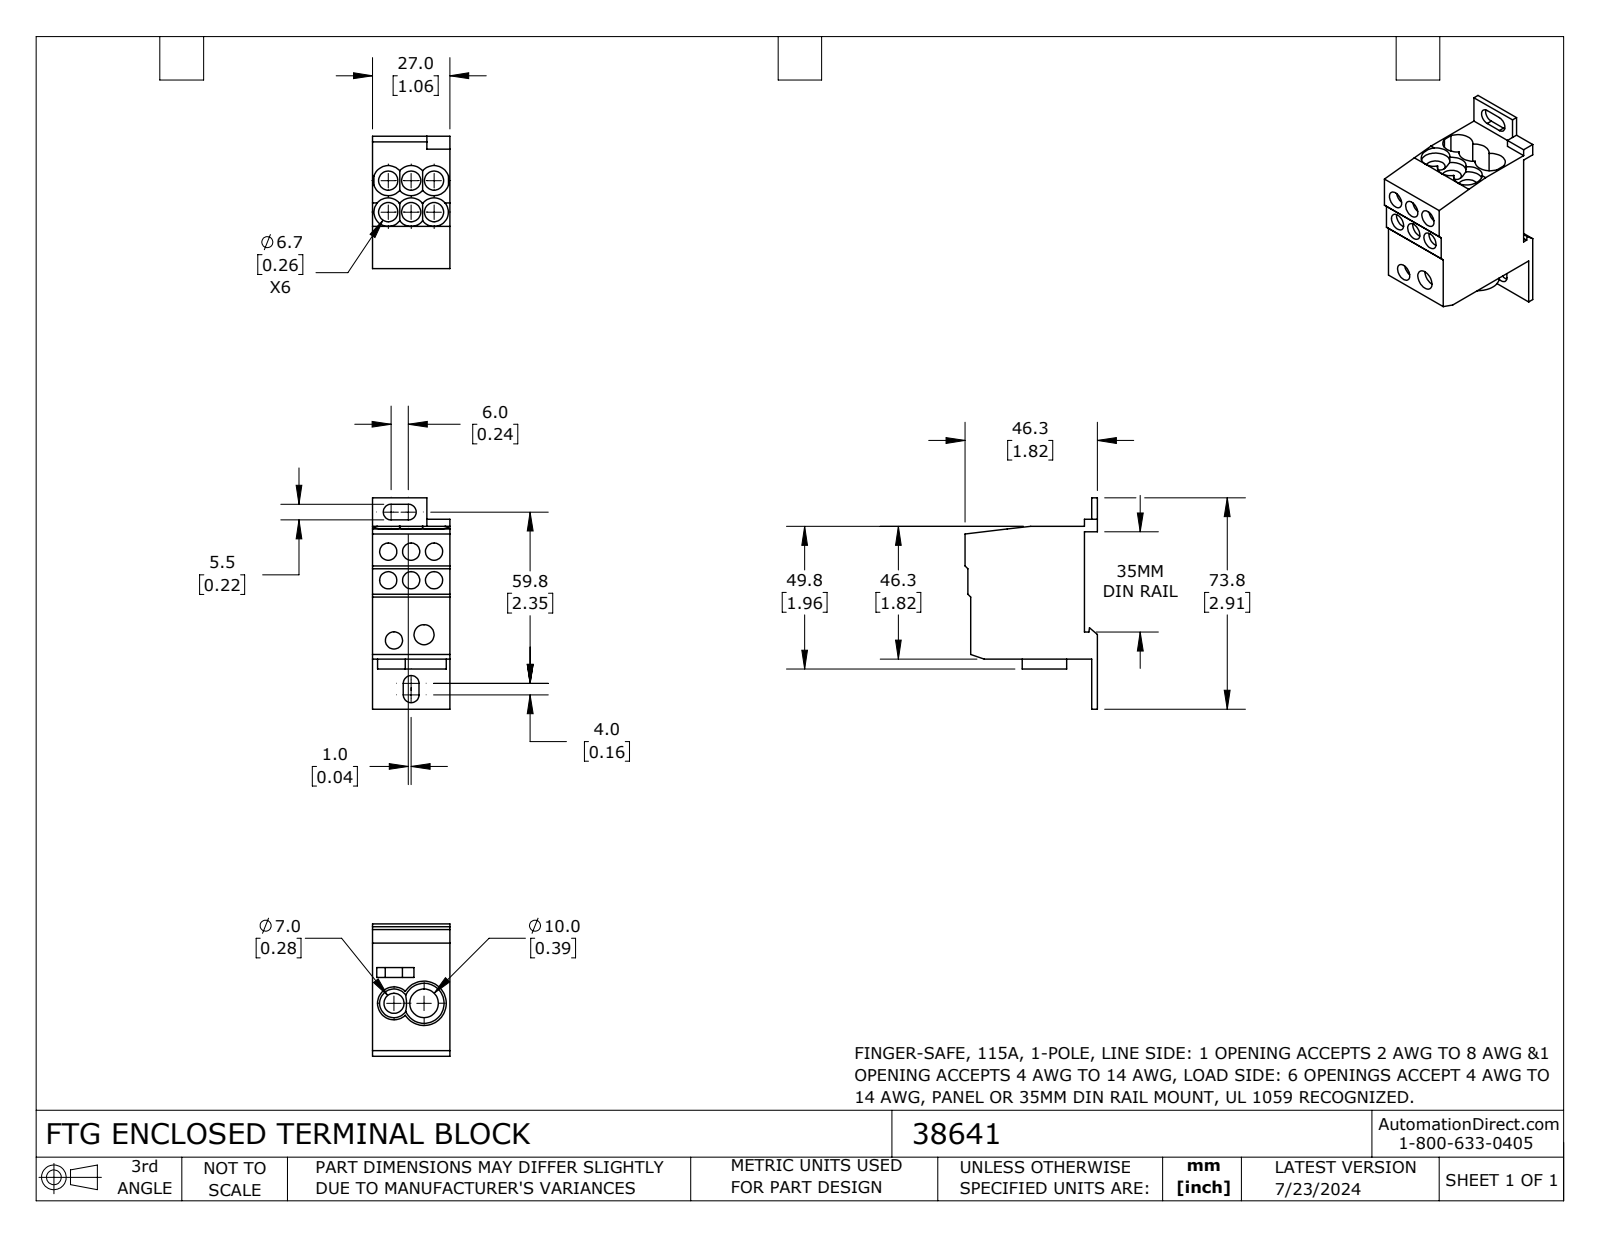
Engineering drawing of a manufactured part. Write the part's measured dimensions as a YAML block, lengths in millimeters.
part_name: "38641"
step_written_by: "SolidWorks 2023 (CONFIG_CONTROL_DESIGN)"
units: millimeters
bodies: {solids: 1, faces: 131, planar: 62, cylindrical: 53, other: 16}
overall_size: [73.8, 46.3, 27]
volume: 42920
surface_area: 15170
round_holes:
  - {diameter: 6, count: 7}
  - {diameter: 6.7, count: 6}
  - {diameter: 10, count: 3}
  - {diameter: 7, count: 2}
round_bosses_or_shafts:
  - {diameter: 15.5, count: 1}
  - {diameter: 6, count: 1}
partial_cylinders:
  - {radius: 2.7, count: 4}
  - {radius: 5.3, count: 3}
  - {radius: 5, count: 1}
  - {radius: 5.7, count: 1}
face_to_face_distances: [27, 4.5, 2.5, 2, 44.2, 3.5, 42.2, 39.8, 1, 40.7]
hole_center_spacings: [8, 10, 12.8, 13.6, 16, 11, 18.9, 19.4]
